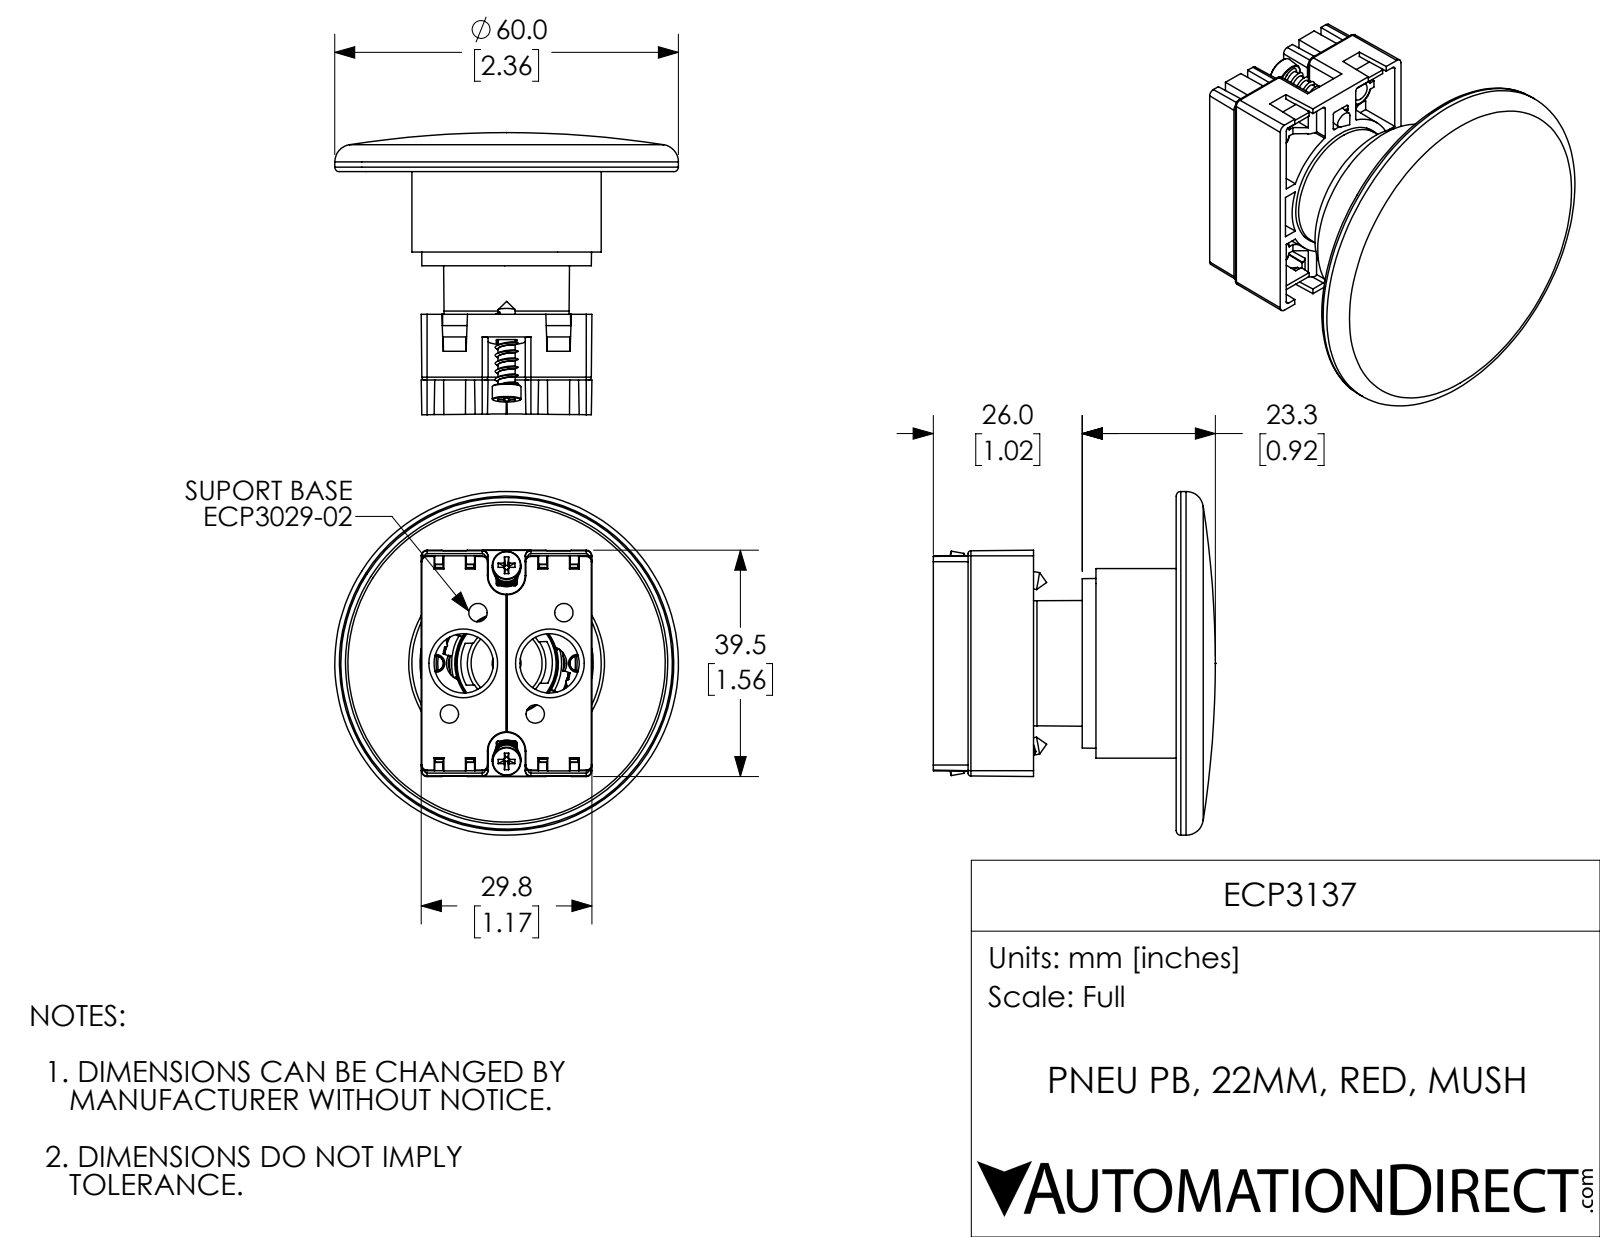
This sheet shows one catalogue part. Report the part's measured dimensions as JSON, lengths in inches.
{"part_name": "ECP3137", "step_written_by": "SolidWorks 2017 (AUTOMOTIVE_DESIGN)", "units": "inches", "bodies": {"solids": 7, "faces": 811, "planar": 368, "cylindrical": 149, "other": 294}, "overall_size": [2.362, 2.362, 1.939], "volume_in3": 1.854, "surface_area_in2": 43.44, "round_holes": [[0.081, 4], [0.407, 2], [0.104, 1], [0.12, 1], [0.697, 1], [0.756, 1], [0.893, 1], [1.191, 1], [2.215, 1]], "round_bosses_or_shafts": [[0.197, 2], [0.118, 2], [2.362, 1], [1.302, 1], [0.86, 1], [0.754, 1], [0.54, 1], [0.488, 1]], "partial_cylinders_radius": [[0.02, 18], [0.006, 8], [0.012, 8], [0.008, 4], [0.039, 4], [0.008, 2], [0.118, 2], [0.128, 2]], "face_to_face_distances": [1.193, 0.067, 0.715, 0.742, 0.451, 0.587, 0.519, 1.37, 0.628, 0.177], "hole_center_spacings": [0.304, 0.541, 0.817, 0.295, 0.472, 0.972, 1.081, 0.591]}
